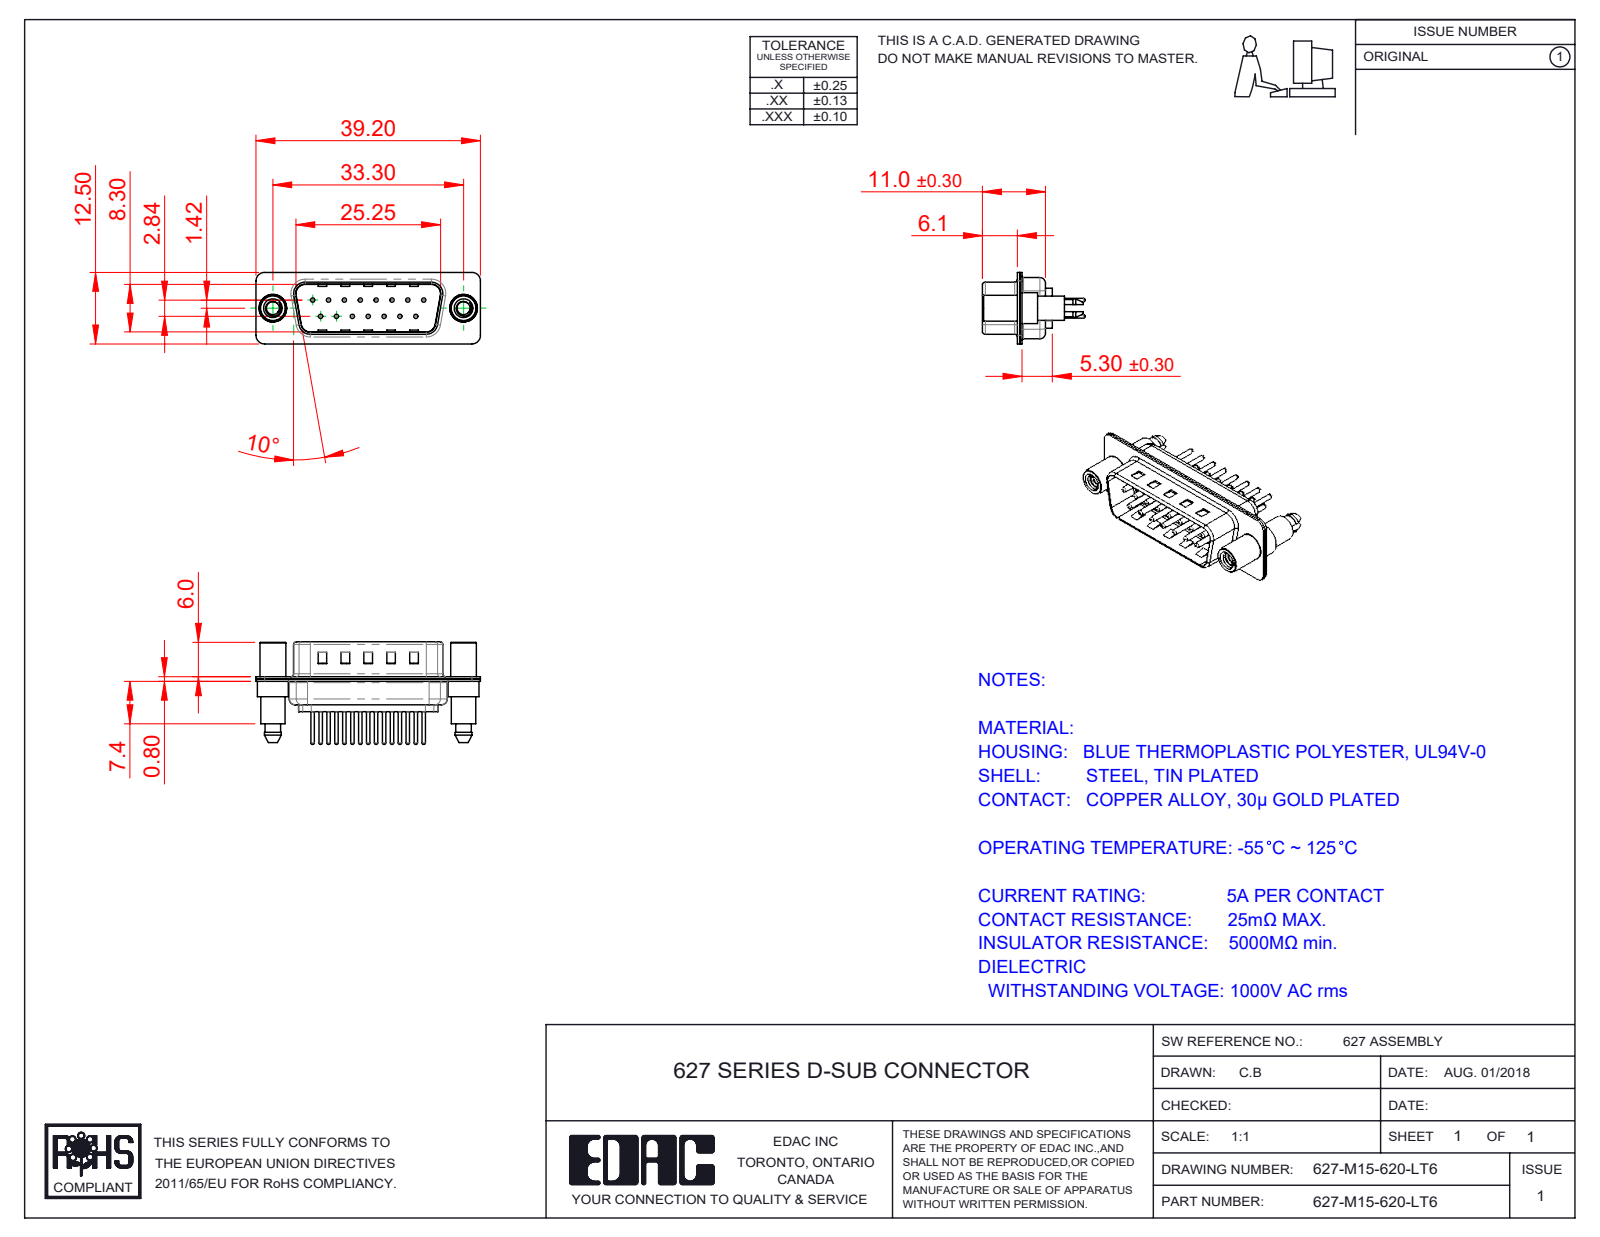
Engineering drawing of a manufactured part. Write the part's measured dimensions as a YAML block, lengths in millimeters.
part_name: "627M Contact Row 2_20; 627M Shell Rear_15 Contacts; 627-M15-620-LT6; 627M Housing_15 Contacts (+3 more)"
step_written_by: "SolidWorks 2020 (CONFIG_CONTROL_DESIGN)"
units: millimeters
bodies: {solids: 20, faces: 947, planar: 262, cylindrical: 371, other: 314}
overall_size: [39.2, 17.9, 12.5]
volume: 2182
surface_area: 5276
round_holes:
  - {diameter: 0.75, count: 15}
  - {diameter: 1.6, count: 15}
  - {diameter: 2, count: 15}
  - {diameter: 2.26, count: 2}
  - {diameter: 4, count: 2}
  - {diameter: 4.8, count: 2}
round_bosses_or_shafts:
  - {diameter: 1.5, count: 15}
  - {diameter: 0.6, count: 15}
  - {diameter: 5.4, count: 2}
  - {diameter: 4.9, count: 2}
  - {diameter: 4.5, count: 2}
  - {diameter: 4.25, count: 2}
partial_cylinders:
  - {radius: 1.5, count: 18}
  - {radius: 2, count: 12}
  - {radius: 1.6, count: 10}
  - {radius: 0.5, count: 8}
  - {radius: 0.25, count: 4}
  - {radius: 0.6, count: 4}
  - {radius: 0.65, count: 4}
  - {radius: 0.9, count: 4}
face_to_face_distances: [0.4, 0.8, 9.5, 9.1, 8.7, 9.9, 5.3, 1.2, 6.1, 5.7]
hole_center_spacings: [3.16, 2.77, 5.54, 8.31, 11.08, 5.03, 5.04, 7.48]
